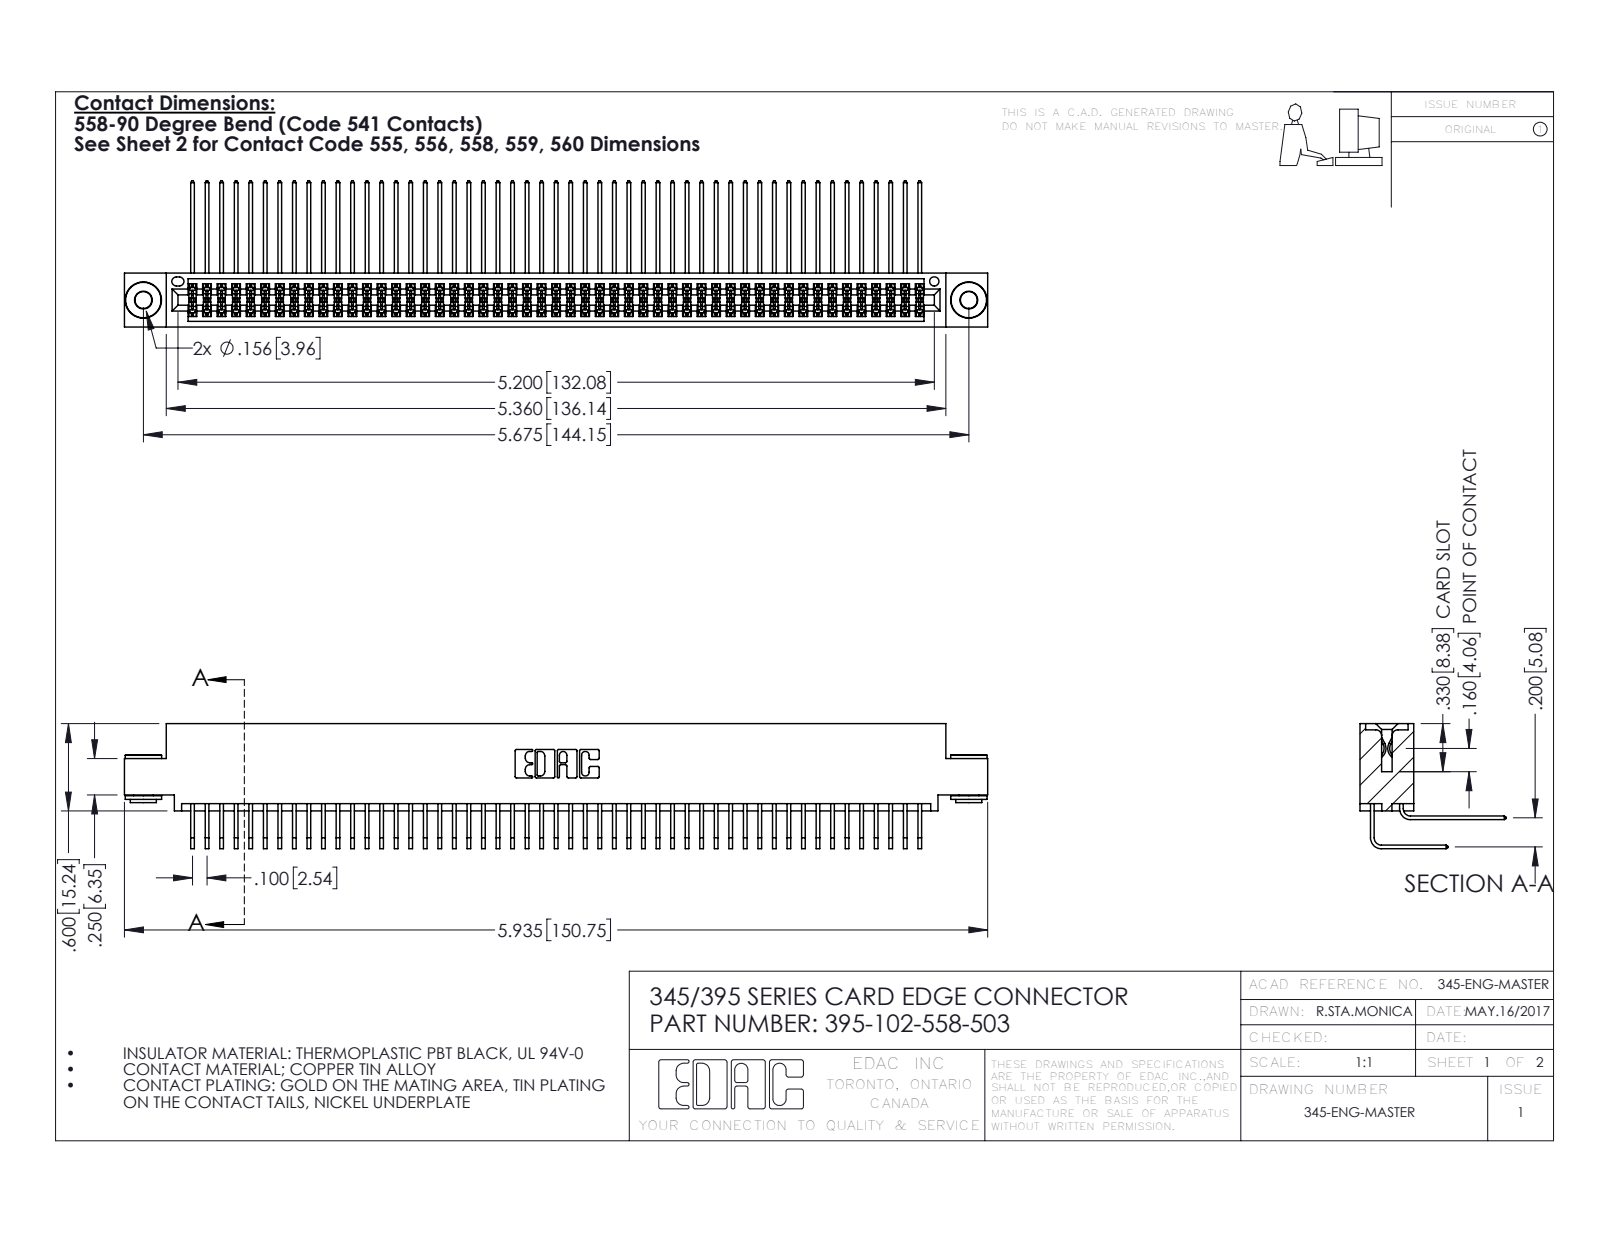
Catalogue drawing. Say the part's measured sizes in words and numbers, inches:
The part is named "345-292-001_558 559 Tail - 1; 395-102-558-503; 345-292-001_558 Tail - 2; 345-250-002_345-250-002-102 (+1 more)". Its 3-D file was written by "SolidWorks 2016 (CONFIG_CONTROL_DESIGN)". It is 105 solids with 5472 faces: 3664 planar, 1800 cylindrical and 8 other. Overall it measures 5.935 by 1.005 by 0.859 inches. Its volume is 0.931 cubic inches and its surface area 39.99 square inches. Round holes: 2 of diameter 0.116, 2 of diameter 0.156, 1 of diameter 0.064. Round bosses or shafts: 2 of diameter 0.25, 2 of diameter 0.18, 2 of diameter 0.136. Partial cylindrical surfaces (rounded edges, fillets, slot ends): 154 of radius 0.006, 22 of radius 0.01, 6 of radius 0.007, 6 of radius 0.031, 3 of radius 0.026, 2 of radius 0.014, 2 of radius 0.019, 2 of radius 0.022. The main face-to-face distances are 0.072, 0.298, 0.2, 0.025, 0.37, 0.098, 0.272, 0.225, 0.025, 0.175. The hole center spacings are 0.27, 5.439, 5.675.
